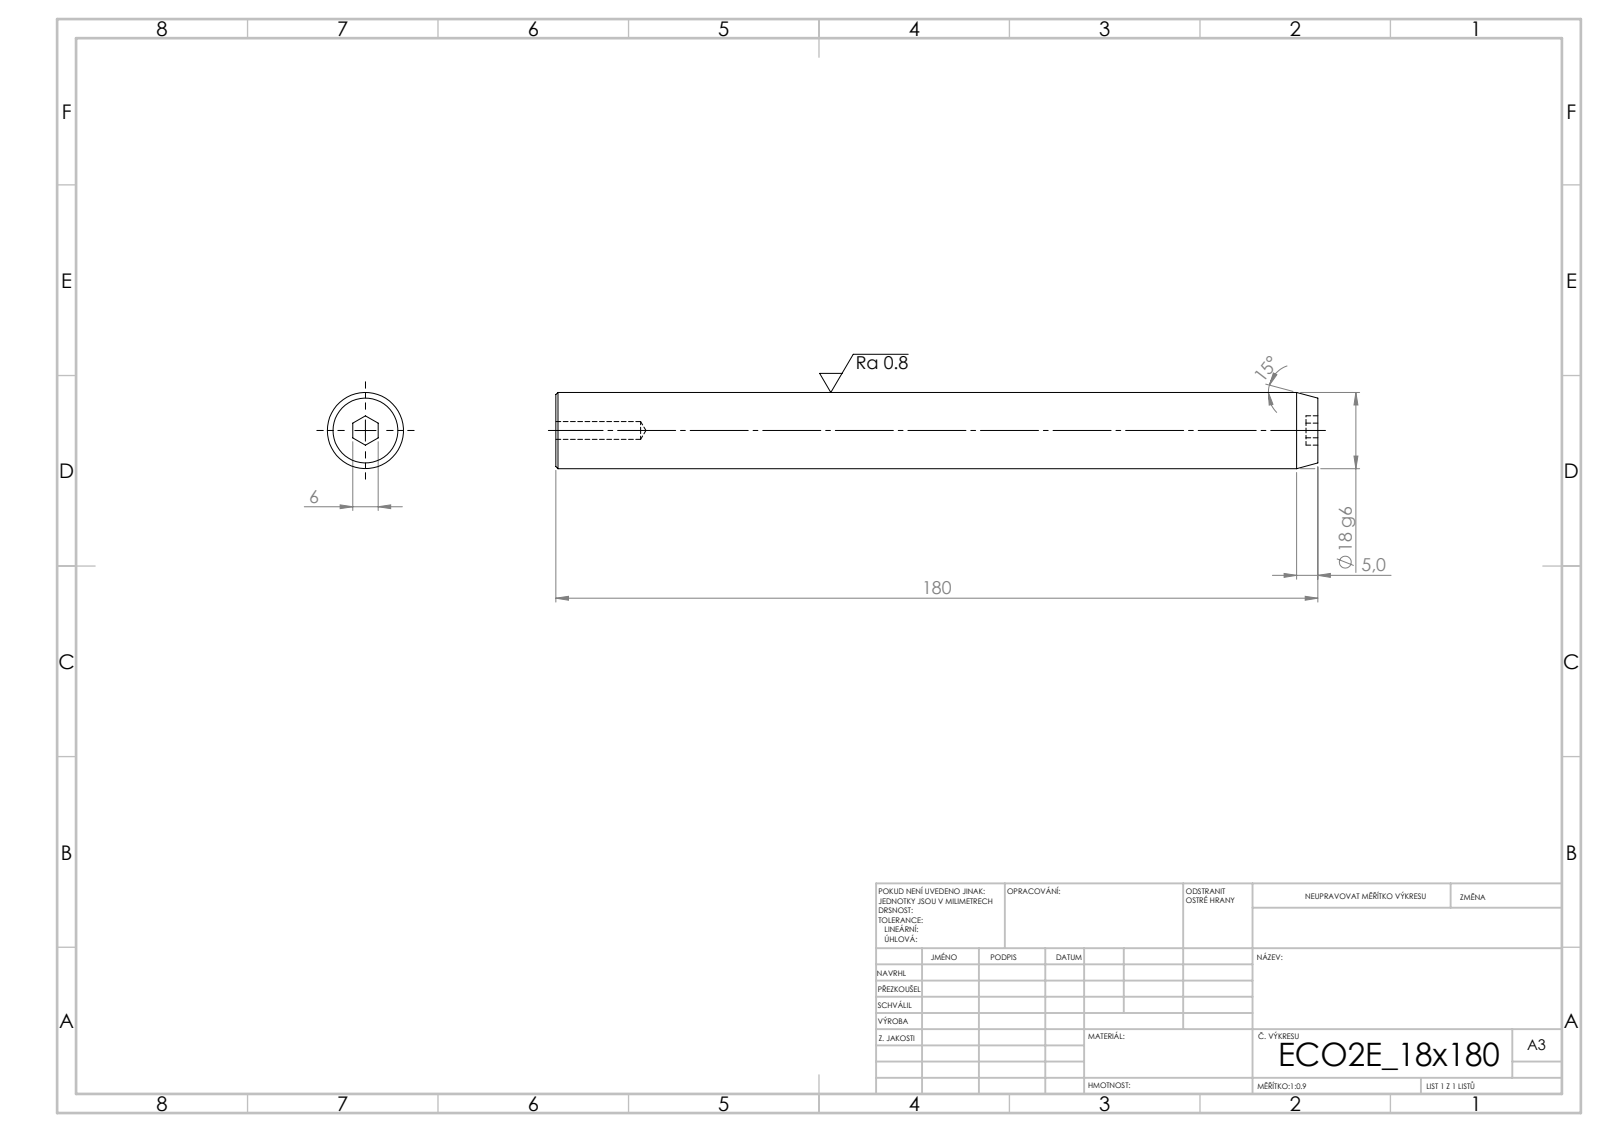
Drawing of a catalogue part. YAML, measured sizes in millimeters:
step_written_by: "SolidWorks 2019 (CONFIG_CONTROL_DESIGN)"
units: millimeters
bodies: {solids: 1, faces: 19, planar: 9, cylindrical: 4, other: 6}
overall_size: [180, 18, 18]
volume: 45247
surface_area: 10913
round_holes:
  - {diameter: 4.2, count: 1}
round_bosses_or_shafts:
  - {diameter: 18, count: 1}
face_to_face_distances: [180, 2.8, 177.2, 6]
